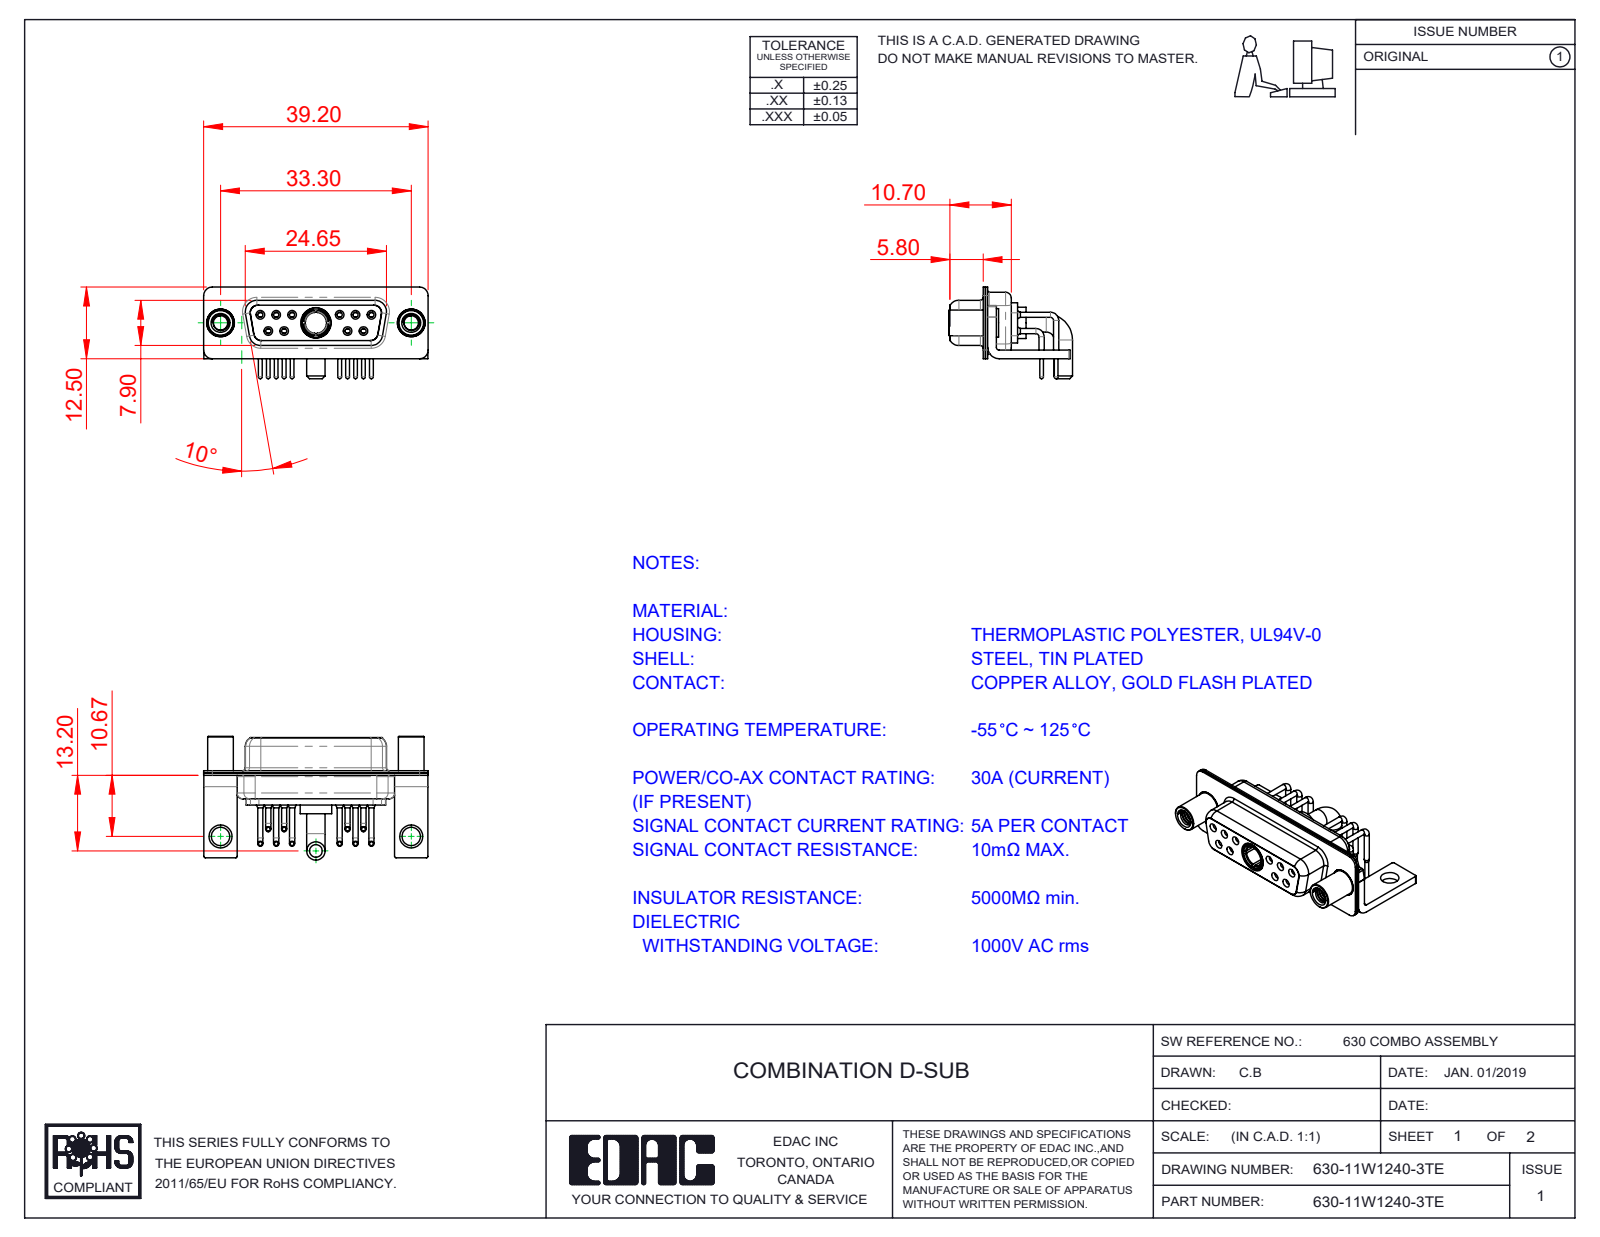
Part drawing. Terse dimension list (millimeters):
name: Power Socket_30A RA; 630Combo Contact Row 2; 630-11W1240-3TE; 630Combo Threaded Standoff_D (+5 more)
written by: SolidWorks 2020 (CONFIG_CONTROL_DESIGN)
unit: mm
bodies: 19 solids, 985 faces (268 planar, 464 cylindrical, 253 other)
size: 39.2 × 21.6 × 16
volume: 3 058 mm³; area: 7 215 mm²
holes: 10× ⌀0.9, 10× ⌀1.1, 10× ⌀1.5, 10× ⌀2, 6× ⌀1.7, 4× ⌀1.6, 3× ⌀4.85, 2× ⌀2.5, 2× ⌀3.2, 2× ⌀4, 2× ⌀4.05, 1× ⌀3.7
bosses: 10× ⌀0.9, 10× ⌀0.65, 6× ⌀1.6, 2× ⌀5, 2× ⌀4.95, 2× ⌀4.8, 2× ⌀4.5, 2× ⌀3.2
rounds: 16× R0.25, 16× R1.5, 13× R2, 12× R1.35, 8× R1.6, 5× R0.5, 4× R0.6, 4× R0.65
face distances: 0.4, 0.8, 1.4, 0.45, 8.45, 1.5, 1.8, 8.9, 6.2, 2.3
hole spacings: 3.16, 2.77, 13.85, 11.08, 16.62, 5.03, 5.04, 5.54
